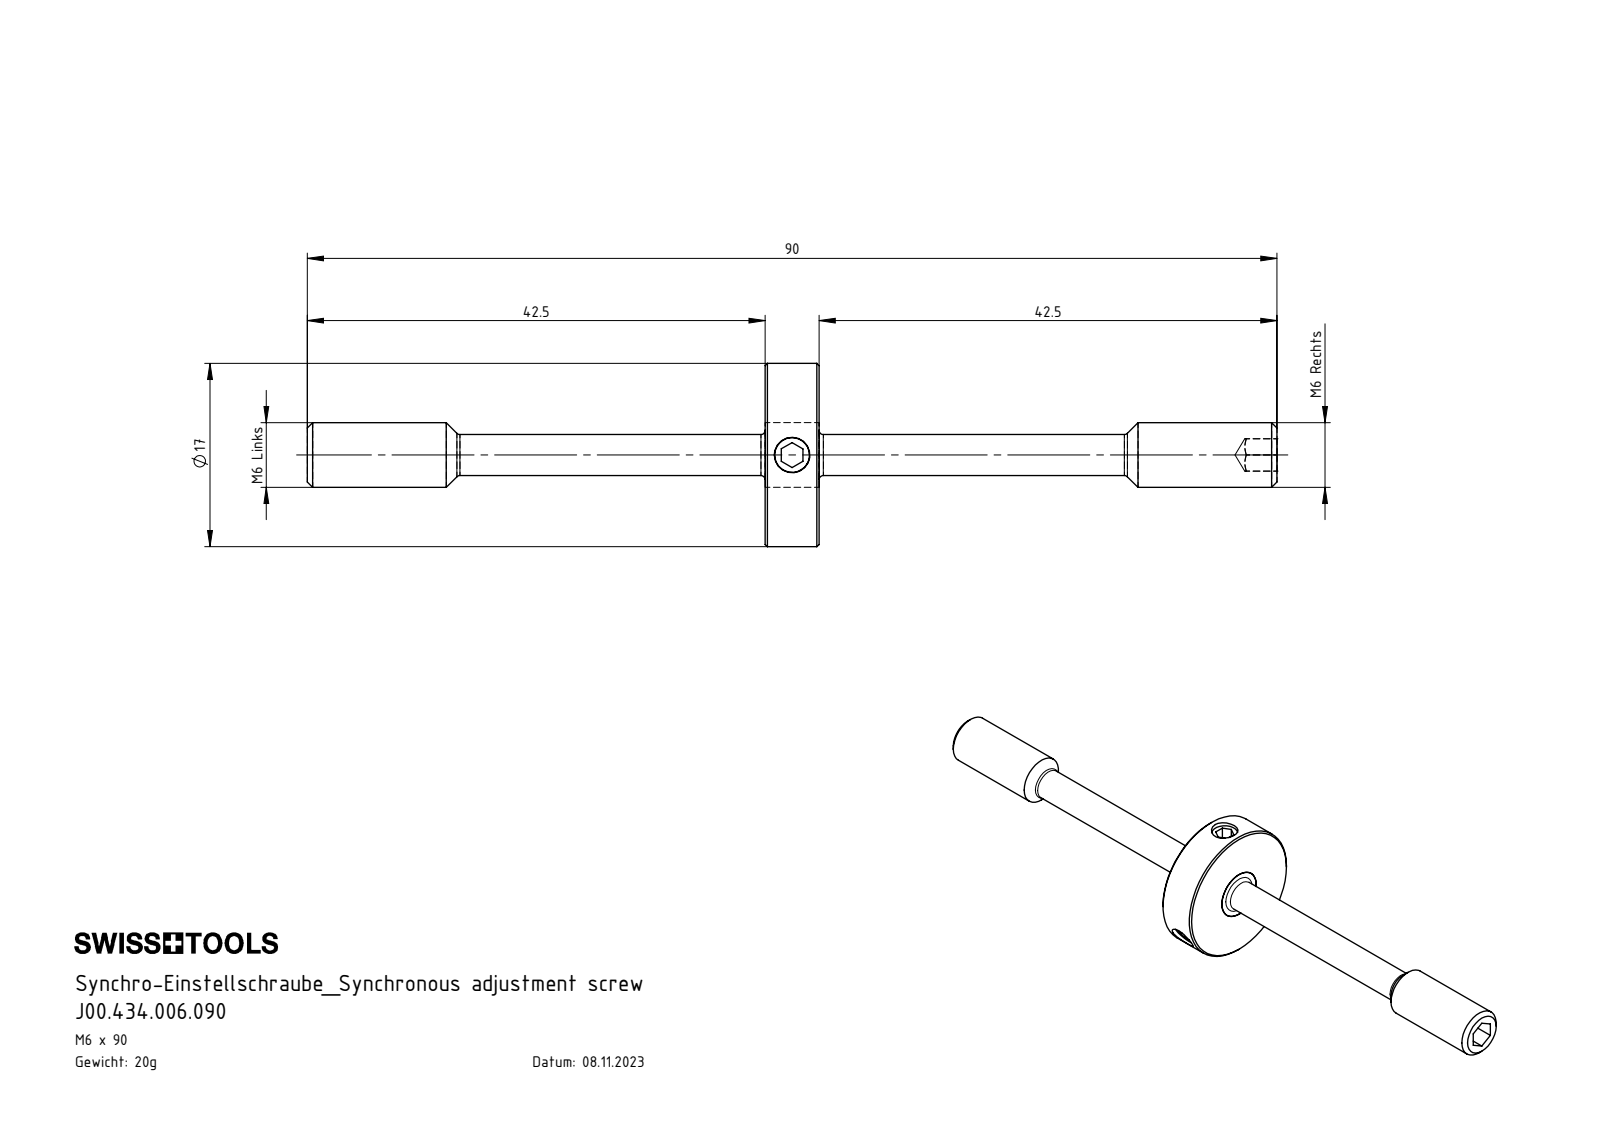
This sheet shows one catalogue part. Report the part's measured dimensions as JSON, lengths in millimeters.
{"part_name": "ISO 4026 - M4 x 5; Z42-ER3.002.005_A; J00.434.006.090; Z94-ER3.001.090_A", "step_written_by": "SolidWorks 2022 (AUTOMOTIVE_DESIGN)", "units": "millimeters", "bodies": {"solids": 5, "faces": 99, "planar": 39, "cylindrical": 26, "other": 34}, "overall_size": [90, 17, 17], "volume_mm3": 2530, "surface_area_mm2": 2576, "round_holes": [[3.3, 3]], "round_bosses_or_shafts": [[4, 3], [17, 1], [6, 1], [3.8, 1]], "face_to_face_distances": [5, 42.5, 47.5, 2, 2.5, 3, 90, 44, 46, 1.5]}
